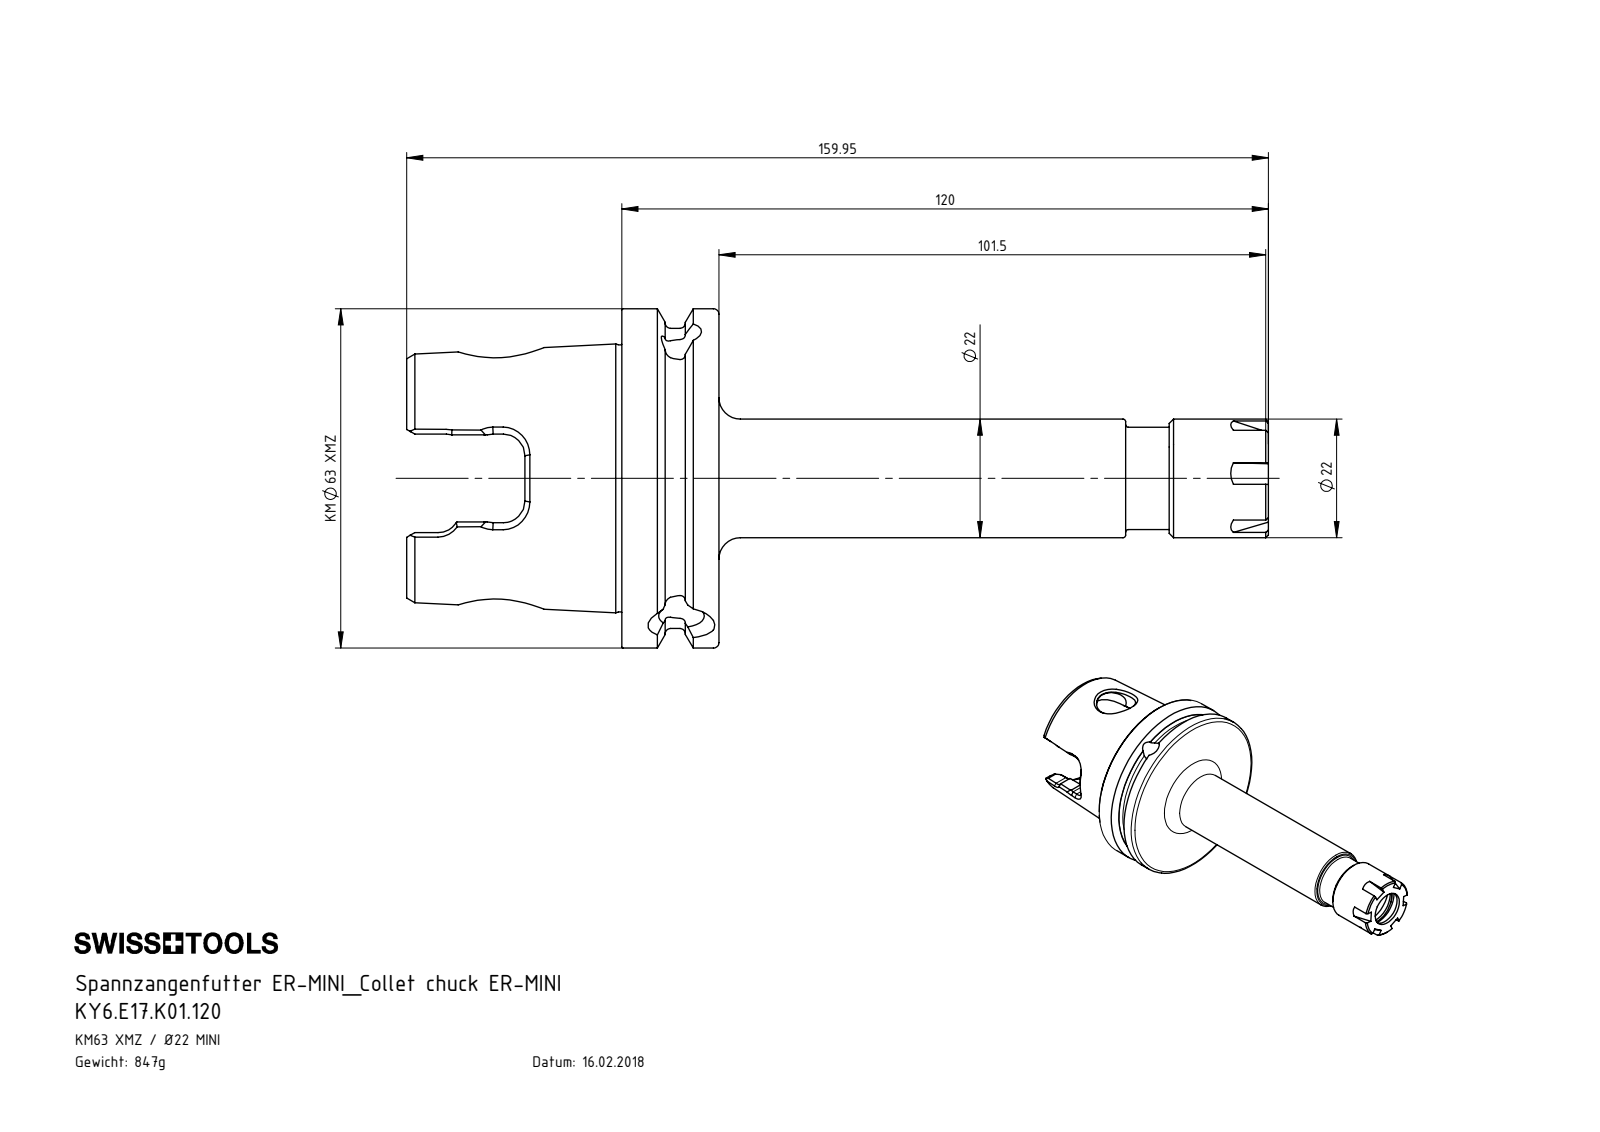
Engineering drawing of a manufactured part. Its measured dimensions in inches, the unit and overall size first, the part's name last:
Units: inches
Overall size (bounding box): 6.297 × 2.478 × 2.478
Round holes (diameter × count): ⌀0.294 ×2, ⌀0.197 ×1, ⌀0.315 ×1, ⌀0.334 ×1, ⌀0.335 ×1, ⌀0.394 ×1, ⌀0.433 ×1, ⌀0.453 ×1, ⌀0.5 ×1, ⌀0.571 ×1, ⌀0.709 ×1, ⌀0.787 ×1
Round bosses / shafts (diameter × count): ⌀2.478 ×1, ⌀2.193 ×1, ⌀0.866 ×1, ⌀0.748 ×1, ⌀0.354 ×1
Partial cylindrical surfaces — rounded edges, fillets, slot ends (radius × count): R0.157 ×6, R0.277 ×2, R0.303 ×2
Main face-to-face distances: 0.709, 0.043, 0.752, 0.236, 0.193, 0.945, 1.337, 1.53, 1.573, 2.281
Volume: 6.584 in³ · Surface area: 50.34 in²
Bodies: 3 solids, 323 faces (103 planar, 72 cylindrical, 148 other)
Part name (STEP PRODUCT): KY6.E17.K01.120; E17-ER1.001.018; ERU-AN4.K01.020_A; KY6-E17.K01.120_B
STEP written by: SolidWorks 2017 (CONFIG_CONTROL_DESIGN)
